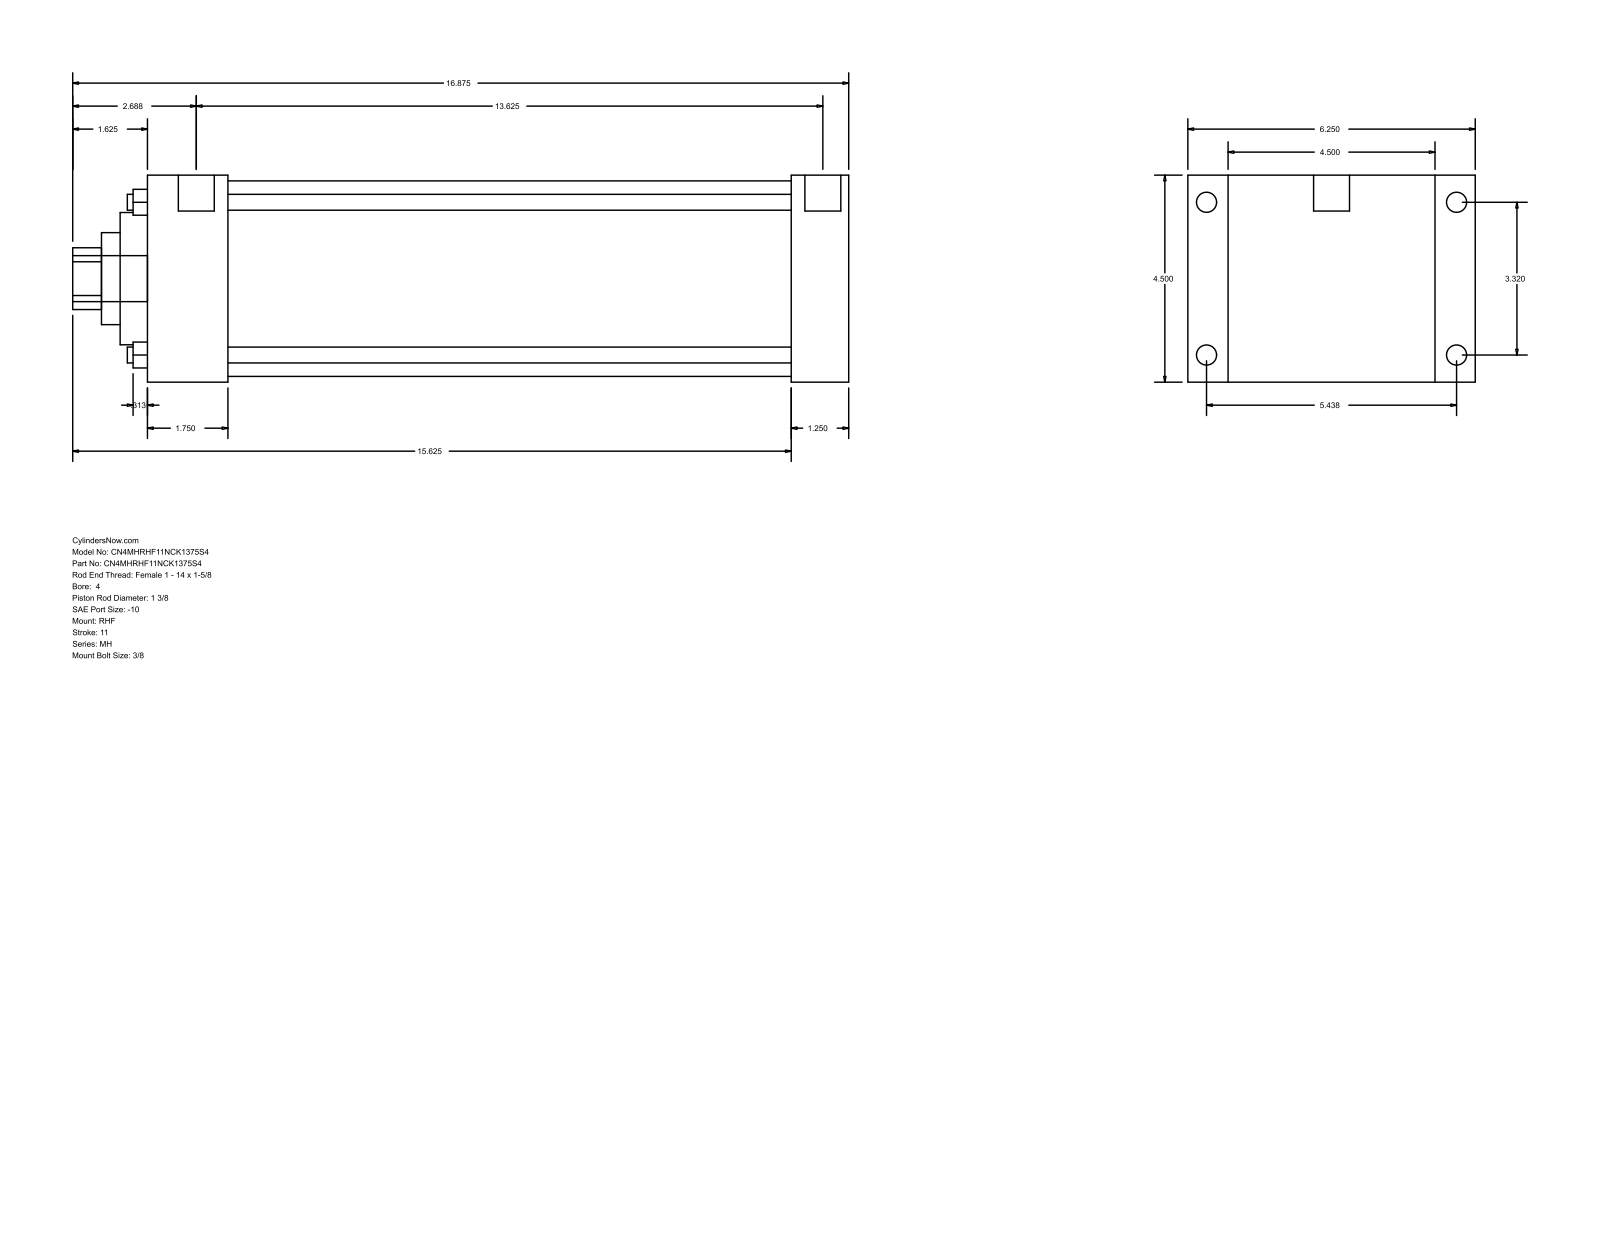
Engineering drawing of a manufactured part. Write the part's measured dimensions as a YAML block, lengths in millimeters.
part_name: "MH_RHF__0400_1.375"
step_written_by: "GSSL Pune (CONFIG_CONTROL_DESIGN)"
units: millimeters
bodies: {solids: 0, faces: 90, planar: 61, cylindrical: 29, other: 0}
overall_size: [428.62, 158.75, 114.3]
round_holes:
  - {diameter: 8.76, count: 4}
  - {diameter: 34.92, count: 1}
  - {diameter: 50.8, count: 1}
  - {diameter: 73.03, count: 1}
  - {diameter: 107.95, count: 1}
round_bosses_or_shafts:
  - {diameter: 11.13, count: 4}
  - {diameter: 8.73, count: 4}
  - {diameter: 19.84, count: 2}
  - {diameter: 25.4, count: 1}
partial_cylinders:
  - {radius: 17.06, count: 1}
face_to_face_distances: [114.3, 387.35, 355.61, 31.74, 22.23, 136.53, 44.45, 311.16, 342.9, 158.76]
hole_center_spacings: [59.62, 84.32, 119.25]
